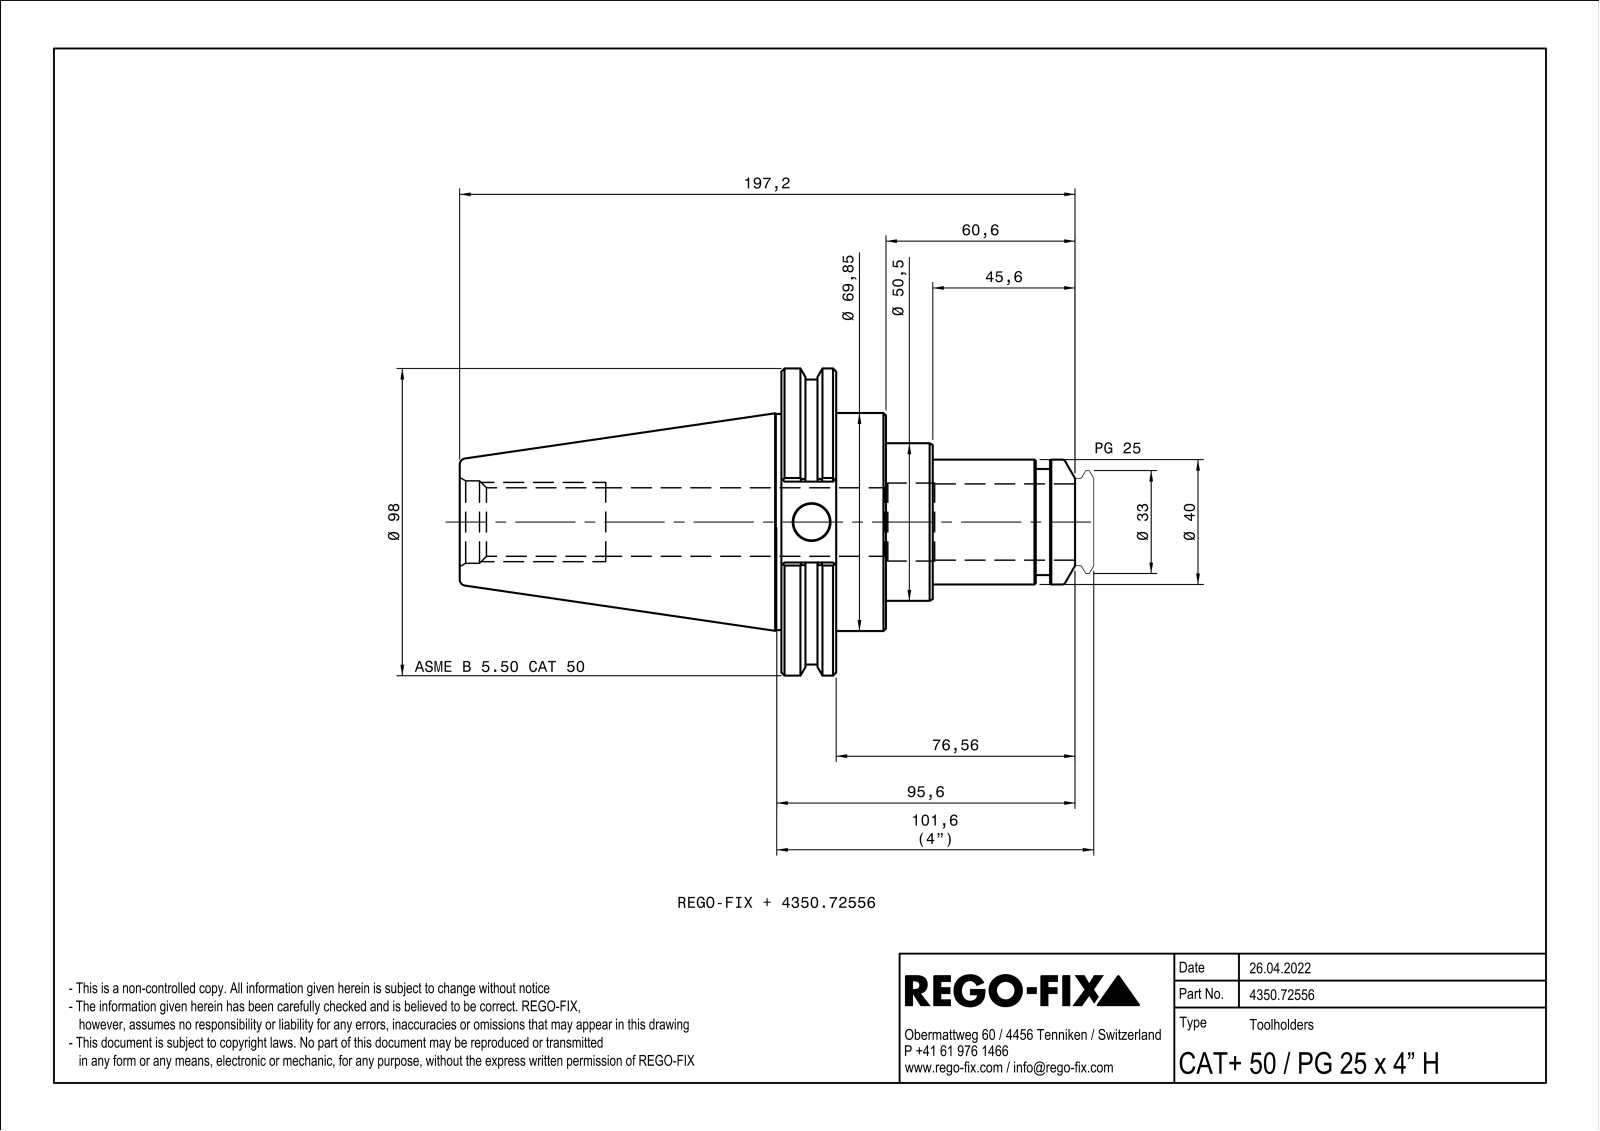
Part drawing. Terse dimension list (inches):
name: NOCUT
written by: SIEMENS PLM Software Solid Edge ST10 (AUTOMOTIVE_DESIGN)
unit: in
bodies: 2 solids, 266 faces (110 planar, 59 cylindrical, 97 other)
size: 7.78 × 3.887 × 3.726
volume: 53.15 in³; area: 193.2 in²
holes: 2× ⌀0.154, 2× ⌀0.177, 1× ⌀0.128, 1× ⌀0.472, 1× ⌀0.865, 1× ⌀0.984, 1× ⌀1.028, 1× ⌀1.039
bosses: 1× ⌀3.887, 1× ⌀3.875, 1× ⌀3.594, 1× ⌀2.762, 1× ⌀2.75, 1× ⌀2.726, 1× ⌀2, 1× ⌀1.988
rounds: 4× R0.02
face distances: 1.329, 0.691, 0.699, 0.63, 1.321, 0.638, 1.337, 5.388, 4.059, 0.591
